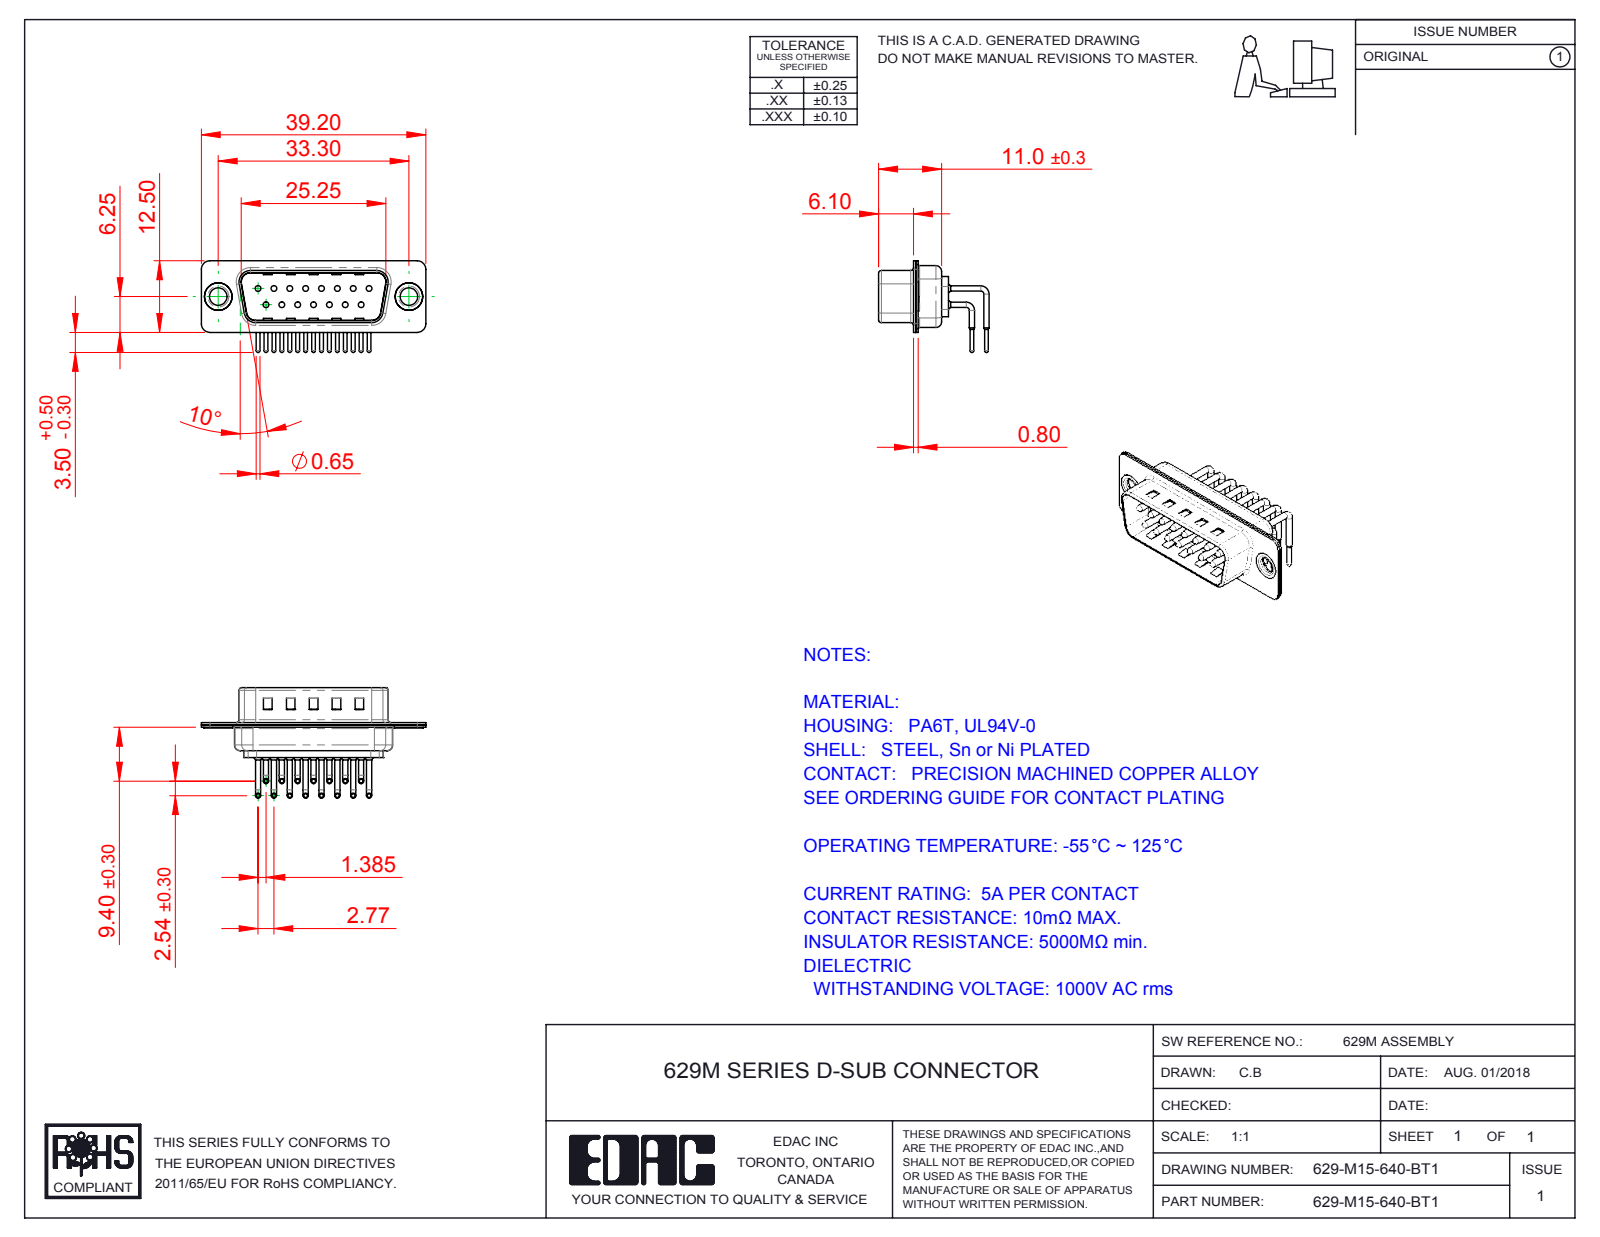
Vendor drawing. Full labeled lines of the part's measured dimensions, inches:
Part name (STEP PRODUCT): 629M Contact Row 1; 629M Contact Row 2; 629M Thru Hole Rivet; 629M Shell Front_15 Contacts (+3 more)
STEP written by: SolidWorks 2016 (CONFIG_CONTROL_DESIGN)
Units: inches
Bodies: 20 solids, 1964 faces (1099 planar, 657 cylindrical, 208 other)
Overall size (bounding box): 1.543 × 0.759 × 0.63
Volume: 0.115 in³ · Surface area: 8.08 in²
Round holes (diameter × count): ⌀0.039 ×15, ⌀0.067 ×15, ⌀0.079 ×15, ⌀0.12 ×2, ⌀0.157 ×2, ⌀0.189 ×2
Round bosses / shafts (diameter × count): ⌀0.035 ×30, ⌀0.059 ×15, ⌀0.026 ×15, ⌀0.197 ×2, ⌀0.193 ×2, ⌀0.14 ×2
Partial cylindrical surfaces — rounded edges, fillets, slot ends (radius × count): R0.059 ×16, R0.04 ×15, R0.079 ×12, R0.02 ×8, R0.063 ×8, R0.01 ×4, R0.024 ×4, R0.026 ×4
Main face-to-face distances: 0.016, 0.033, 0.376, 0.343, 0.049, 0.031, 0.409, 0.059, 0.014, 0.075
Hole centre spacings: 0.124, 0.109, 0.218, 0.327, 0.436, 0.198, 0.198, 0.294
